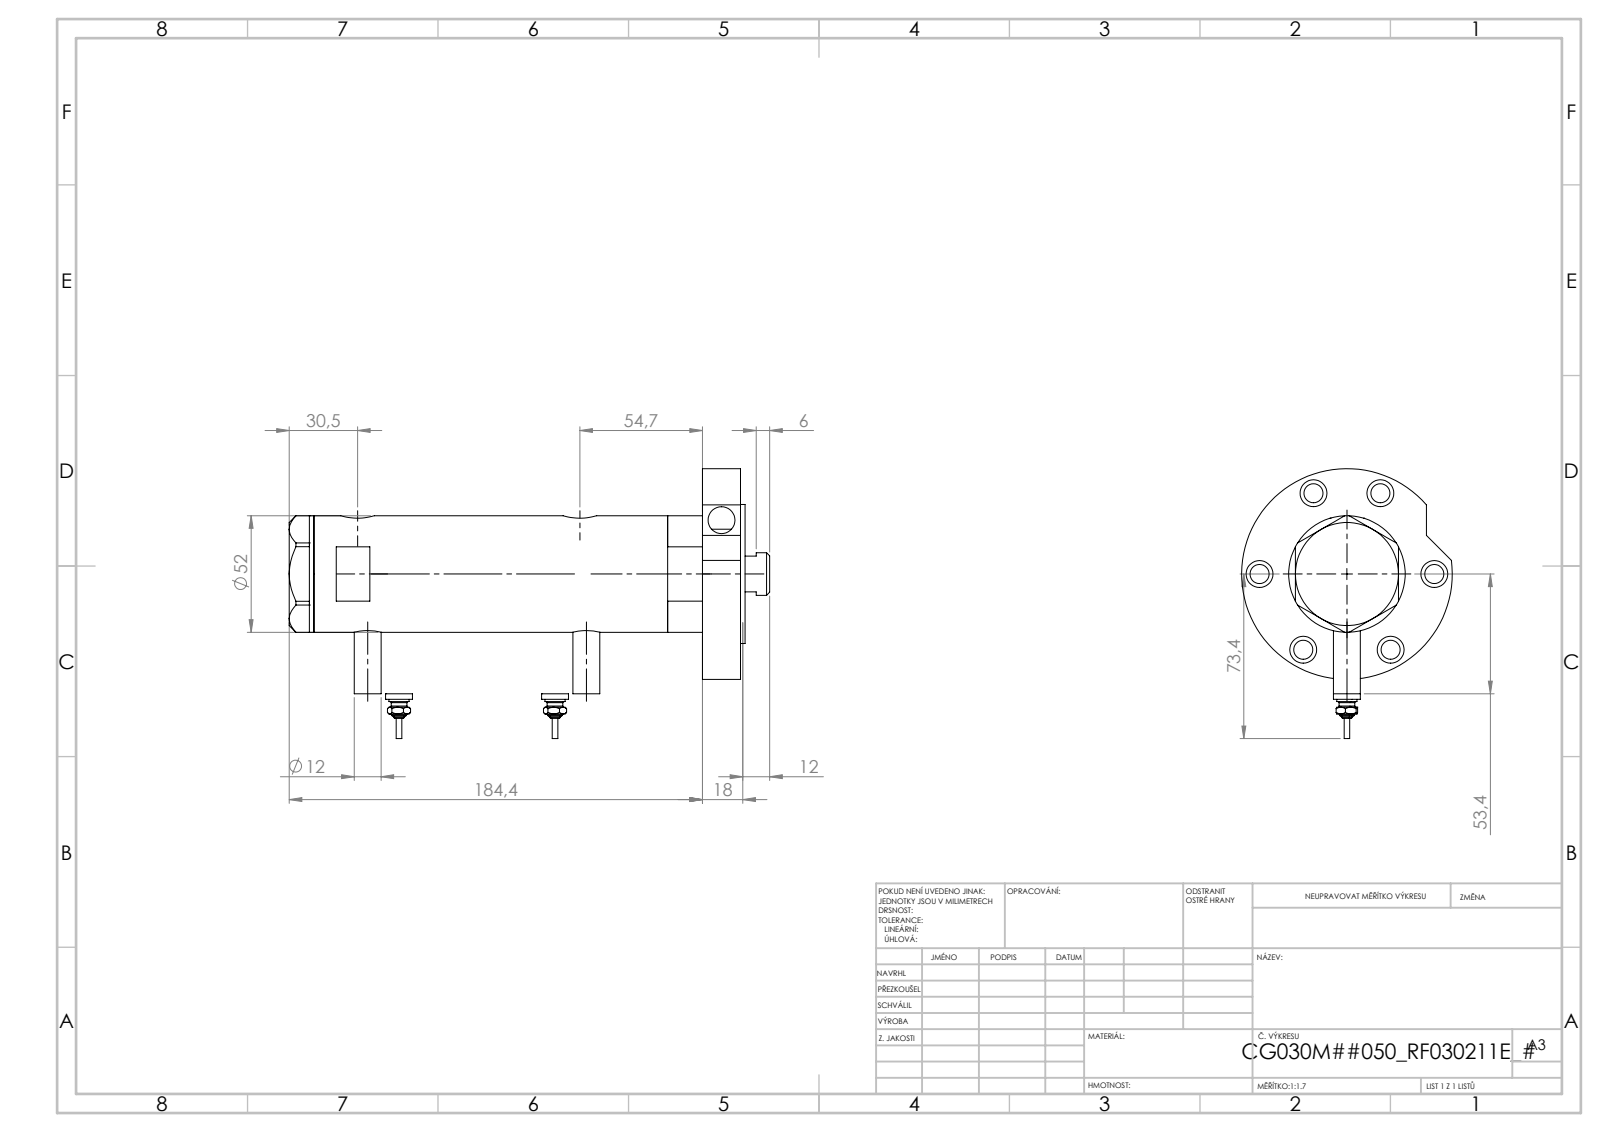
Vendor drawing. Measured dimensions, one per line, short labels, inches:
name: V270CG_FRONT; V270CG_MIDDLE; V270CG_SWITCH; V270CG_BACK (+2 more)
written by: SolidWorks 2019 (CONFIG_CONTROL_DESIGN)
unit: in
bodies: 7 solids, 290 faces (106 planar, 110 cylindrical, 74 other)
size: 7.835 × 4.146 × 3.701
volume: 26.77 in³; area: 165.6 in²
holes: 7× ⌀0.472, 6× ⌀0.335, 2× ⌀0.197, 2× ⌀0.383, 2× ⌀0.492, 2× ⌀0.591, 1× ⌀0.256, 1× ⌀0.787, 1× ⌀0.846, 1× ⌀1.181, 1× ⌀1.299, 1× ⌀1.575
bosses: 3× ⌀0.472, 2× ⌀0.354, 2× ⌀0.276, 2× ⌀0.171, 2× ⌀0.094, 1× ⌀3.701, 1× ⌀2.441, 1× ⌀2.047
face distances: 0.669, 6.12, 6.789, 2.043, 0.079, 6.868, 4.076, 2.713, 2.791, 0.748
hole spacings: 1.535, 0.114, 0.177, 1.706, 2.553, 2.659, 2.754, 3.022
